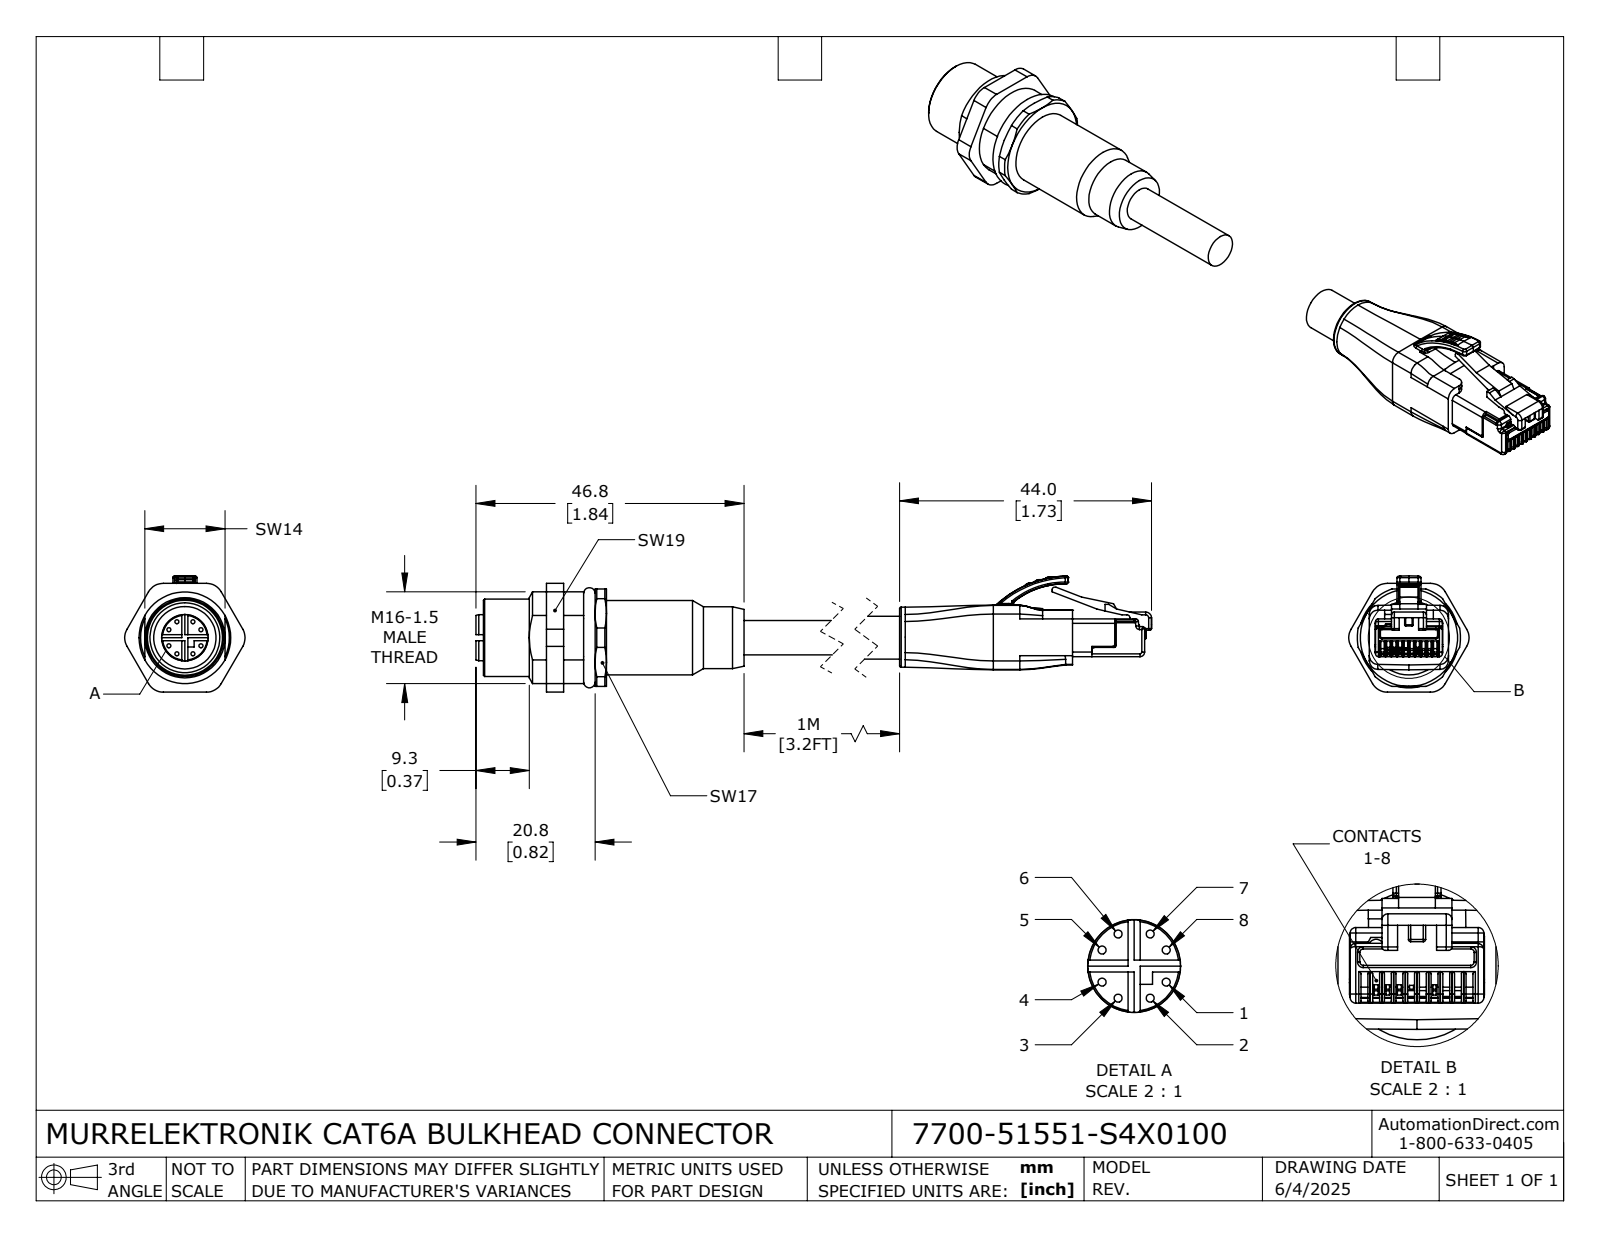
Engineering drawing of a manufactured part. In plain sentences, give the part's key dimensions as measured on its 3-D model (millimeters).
The part is named "7700-51551-S4X0100_BULKHEAD; 7700-51551-S4X0100_RJ45; 7700-51551-S4X0100". Its 3-D file was written by "SolidWorks 2024 (CONFIG_CONTROL_DESIGN)". It is 3 solids with 760 faces: 351 planar, 231 cylindrical and 178 other. Overall it measures 143.8 by 21.01 by 20.29 millimeters. Its volume is 12 565 cubic millimeters and its surface area 6 720 square millimeters. Round holes: 8 of diameter 0.7, 1 of diameter 10.9, 1 of diameter 12.2, 1 of diameter 16. Round bosses or shafts: 1 of diameter 13.5, 1 of diameter 13, 1 of diameter 10.8, 1 of diameter 10.5, 1 of diameter 8.1, 1 of diameter 7.5, 1 of diameter 6. Partial cylindrical surfaces (rounded edges, fillets, slot ends): 61 of radius 0.2, 25 of radius 0.5, 14 of radius 0.3, 9 of radius 1.5, 6 of radius 3, 5 of radius 0.8, 2 of radius 0.54, 2 of radius 5. The main face-to-face distances are 13.9, 6.37, 1.06, 3, 14, 13.8, 10.5, 7.5, 8.5, 1. The hole center spacings are 3.13, 4.43, 1.98, 2.8, 5.6, 5.94, 6.26.
